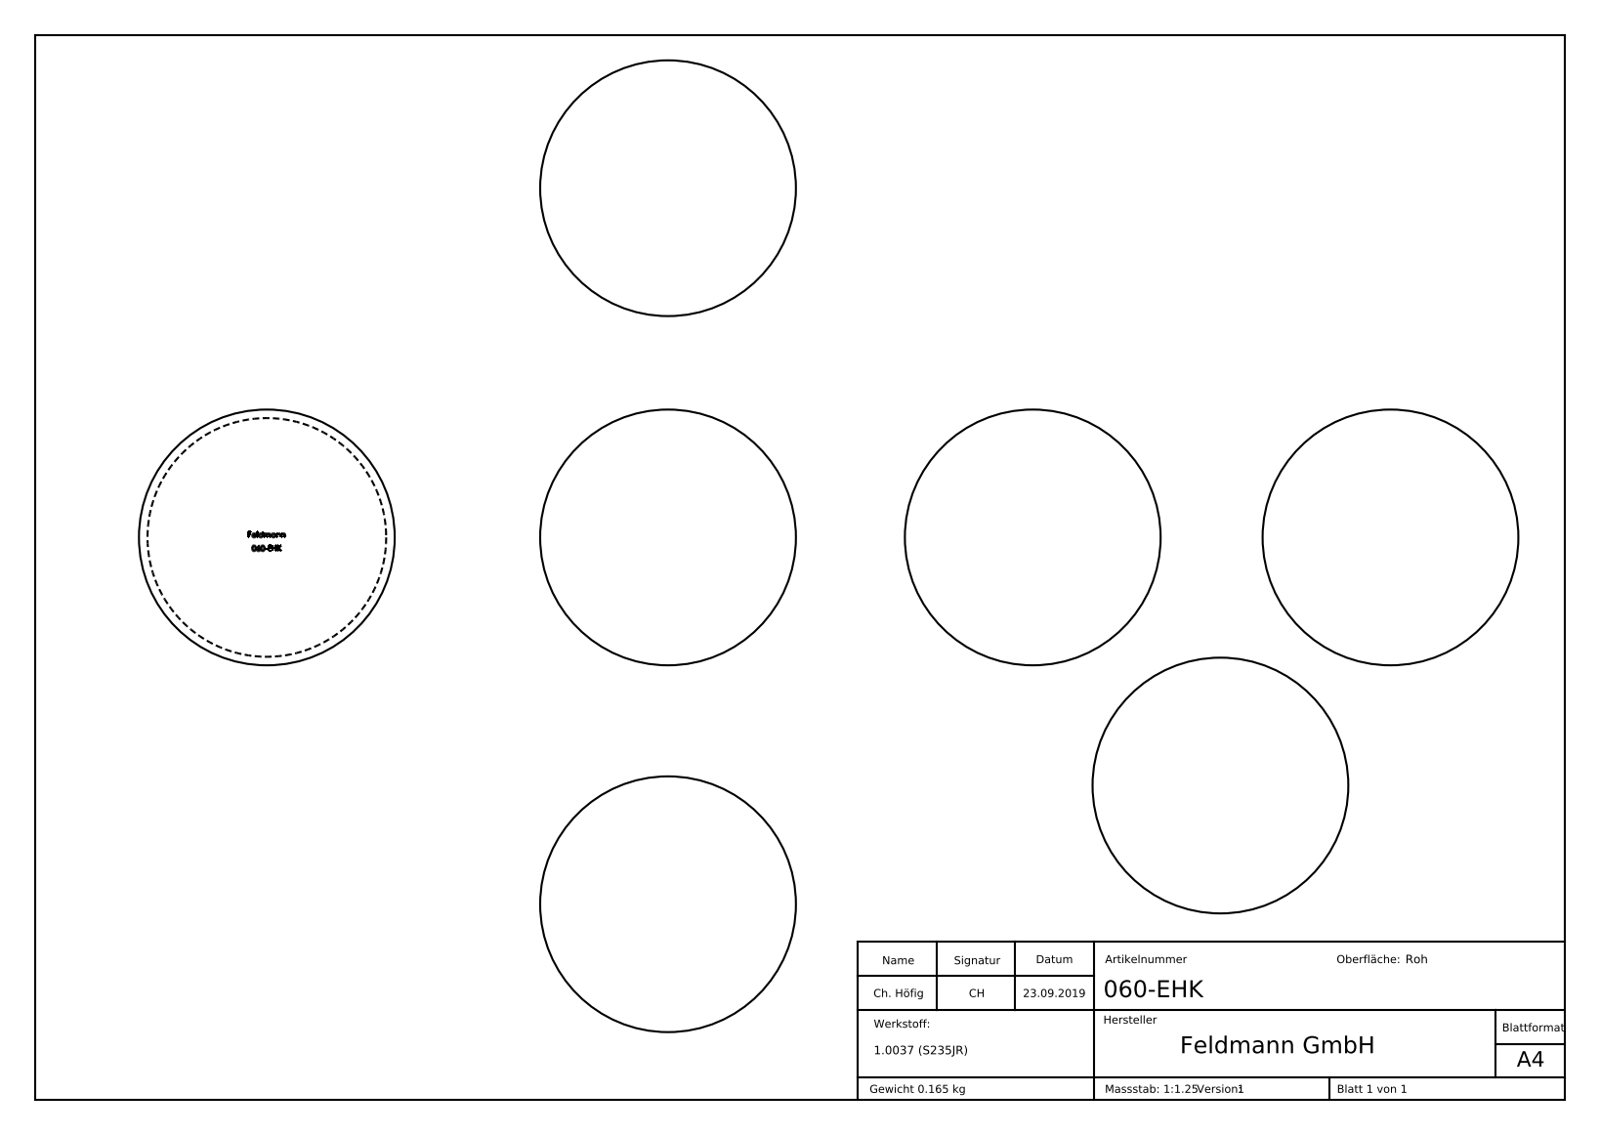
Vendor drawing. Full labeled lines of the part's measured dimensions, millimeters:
Part name (STEP PRODUCT): 060-EHK
STEP written by: SolidWorks 2015 (CONFIG_CONTROL_DESIGN)
Units: millimetres
Bodies: 1 solid, 198 faces (96 planar, 0 cylindrical, 102 other)
Overall size (bounding box): 60 × 60 × 60
Volume: 21 144 mm³ · Surface area: 21 171 mm²
Main face-to-face distances: 3.2, 1.26, 3.13, 4.5, 0.46, 1.35, 3.59, 0.68, 0.64, 3.47
